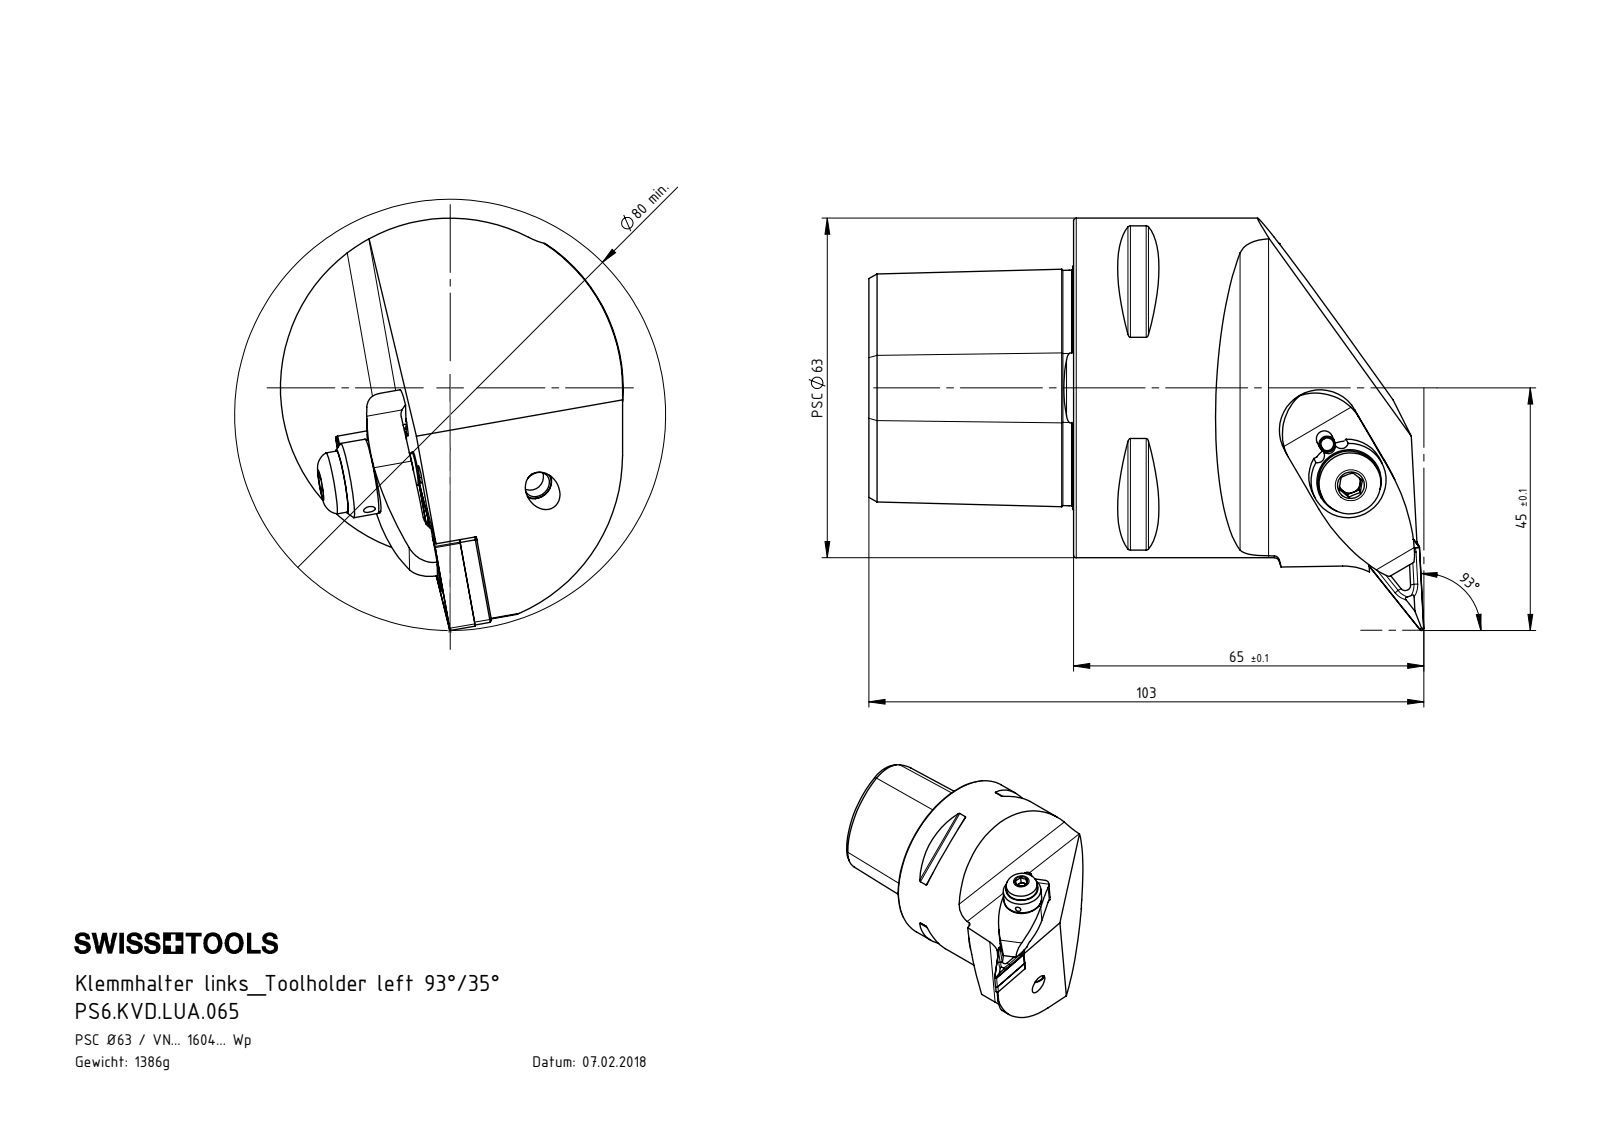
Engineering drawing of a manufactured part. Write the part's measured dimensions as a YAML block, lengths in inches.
part_name: "WCC-ER3.102.029_C; WCC-ER5.102.012_B; WVD-ER2.101.003_A; KVT_MB_600_060 (+6 more)"
step_written_by: "SolidWorks 2017 (AUTOMOTIVE_DESIGN)"
units: inches
bodies: {solids: 10, faces: 425, planar: 100, cylindrical: 131, other: 194}
overall_size: [4.055, 3.012, 2.504]
volume: 10.74
surface_area: 52.02
round_holes:
  - {diameter: 0.079, count: 3}
  - {diameter: 0.197, count: 3}
  - {diameter: 0.276, count: 2}
  - {diameter: 0.094, count: 1}
  - {diameter: 0.118, count: 1}
  - {diameter: 0.13, count: 1}
  - {diameter: 0.15, count: 1}
  - {diameter: 0.157, count: 1}
  - {diameter: 0.195, count: 1}
  - {diameter: 0.236, count: 1}
  - {diameter: 0.244, count: 1}
  - {diameter: 0.272, count: 1}
round_bosses_or_shafts:
  - {diameter: 0.236, count: 2}
  - {diameter: 0.157, count: 2}
  - {diameter: 0.118, count: 2}
  - {diameter: 2.48, count: 1}
  - {diameter: 0.551, count: 1}
  - {diameter: 0.453, count: 1}
  - {diameter: 0.268, count: 1}
  - {diameter: 0.207, count: 1}
partial_cylinders:
  - {radius: 0.02, count: 10}
  - {radius: 0.013, count: 6}
  - {radius: 0.023, count: 6}
  - {radius: 0.016, count: 4}
  - {radius: 0.059, count: 3}
  - {radius: 0.079, count: 2}
  - {radius: 0.118, count: 2}
  - {radius: 0.236, count: 2}
face_to_face_distances: [1.496, 0.98, 0.051, 0.301, 0.125, 0.176, 0.352, 0.227, 1.063, 0.433]
hole_center_spacings: [1.076, 0.316, 0.323, 0.76, 0.753, 0.753, 1.076, 1.083]
